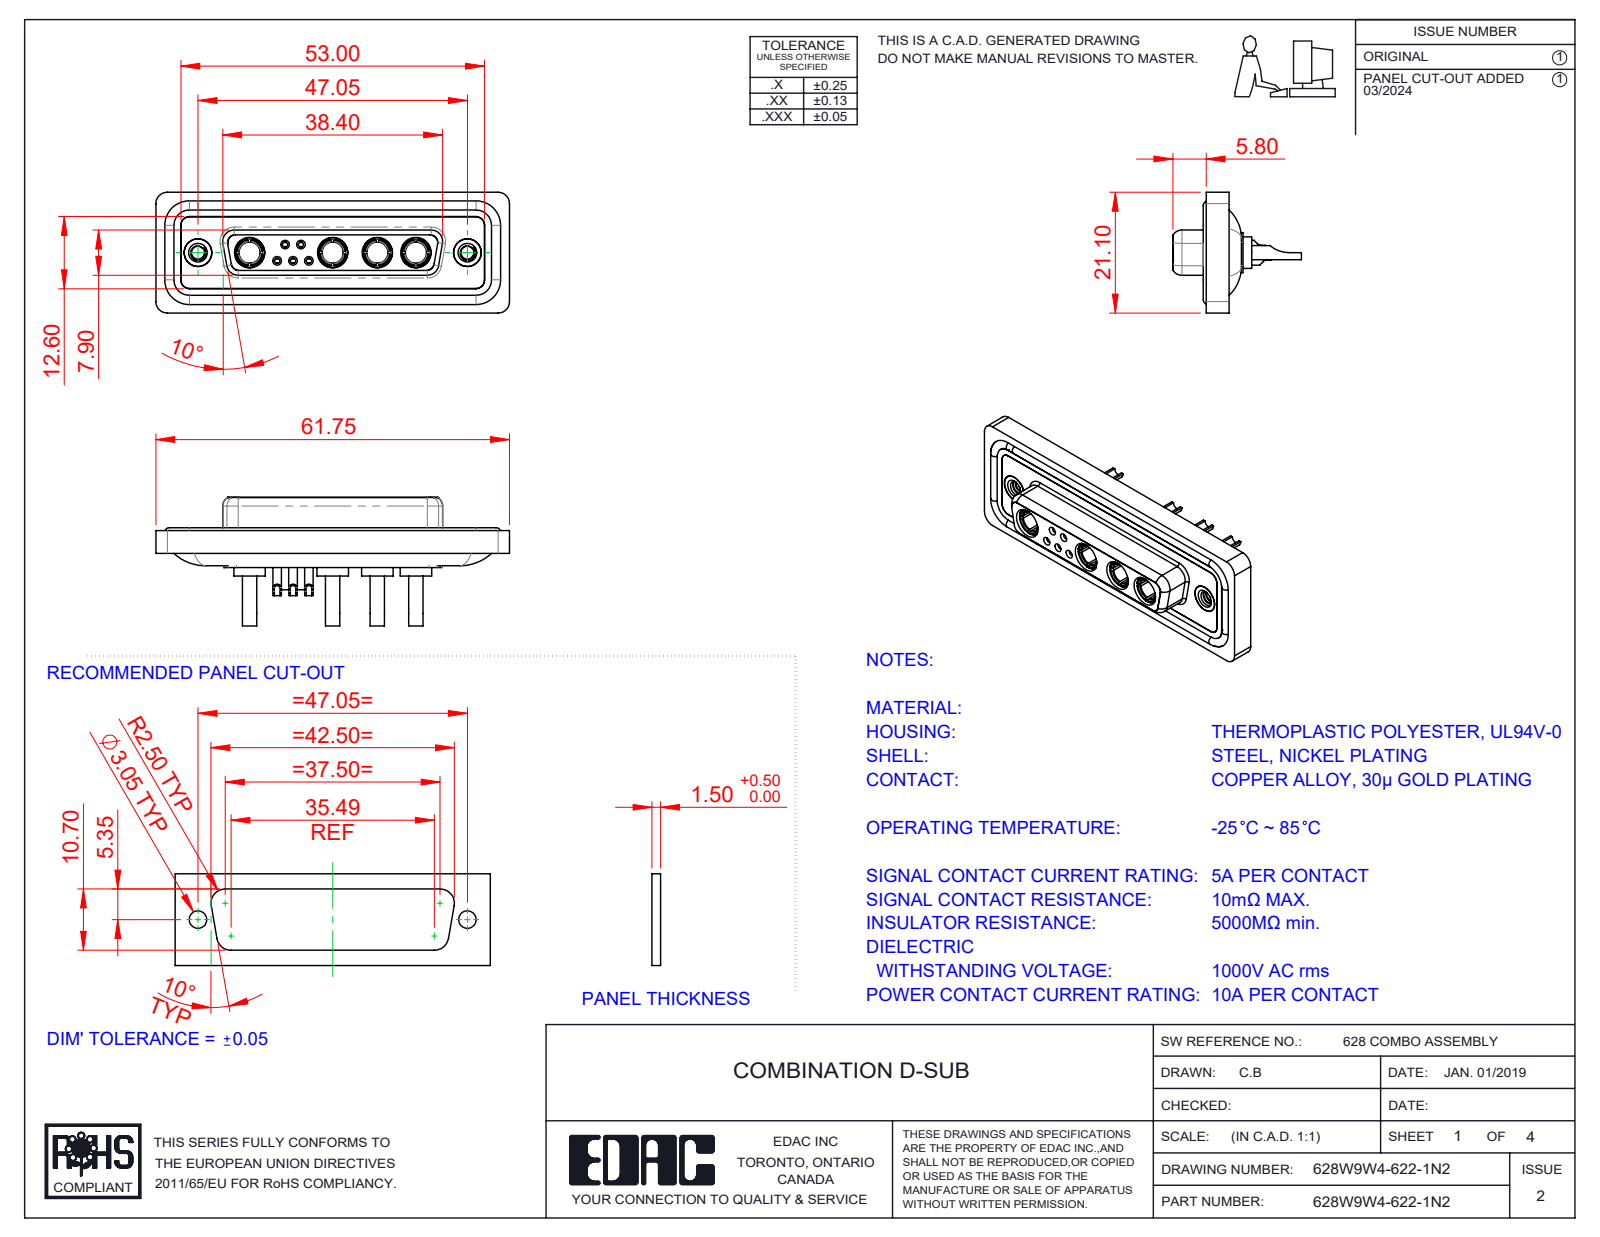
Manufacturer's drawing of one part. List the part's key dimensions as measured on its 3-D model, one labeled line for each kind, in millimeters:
Part name (STEP PRODUCT): 628Combo Waterproof Housing_25 Contacts; 628Combo Threaded Rivet_2; 628Combo Housing_9W4; Power Socket_10A SC (+5 more)
STEP written by: SolidWorks 2023 (CONFIG_CONTROL_DESIGN)
Units: millimetres
Bodies: 20 solids, 977 faces (314 planar, 397 cylindrical, 266 other)
Overall size (bounding box): 61.75 × 22.45 × 21.1
Volume: 8 223 mm³ · Surface area: 13 808 mm²
Round holes (diameter × count): ⌀4.85 ×6, ⌀0.9 ×5, ⌀1 ×5, ⌀1.1 ×5, ⌀1.5 ×5, ⌀2 ×5, ⌀1.7 ×4, ⌀3.7 ×4, ⌀5.3 ×4, ⌀1.6 ×3, ⌀1.7 ×2, ⌀2.26 ×2
Round bosses / shafts (diameter × count): ⌀1.6 ×6, ⌀2.2 ×5, ⌀5.5 ×4, ⌀5.2 ×4, ⌀4.96 ×4, ⌀4.75 ×4, ⌀3.75 ×4, ⌀2.5 ×4
Partial cylindrical surfaces — rounded edges, fillets, slot ends (radius × count): R1.5 ×22, R2 ×18, R1.35 ×8, R1.6 ×8, R1 ×6, R0.25 ×4, R0.5 ×4, R0.6 ×4
Main face-to-face distances: 0.4, 1.8, 7.45, 5.65, 0.5, 7.05, 6.6, 1.6, 1.1, 2.9
Hole centre spacings: 3.16, 2.77, 5.03, 2.76, 4.4, 5.02, 5.54, 5.73
